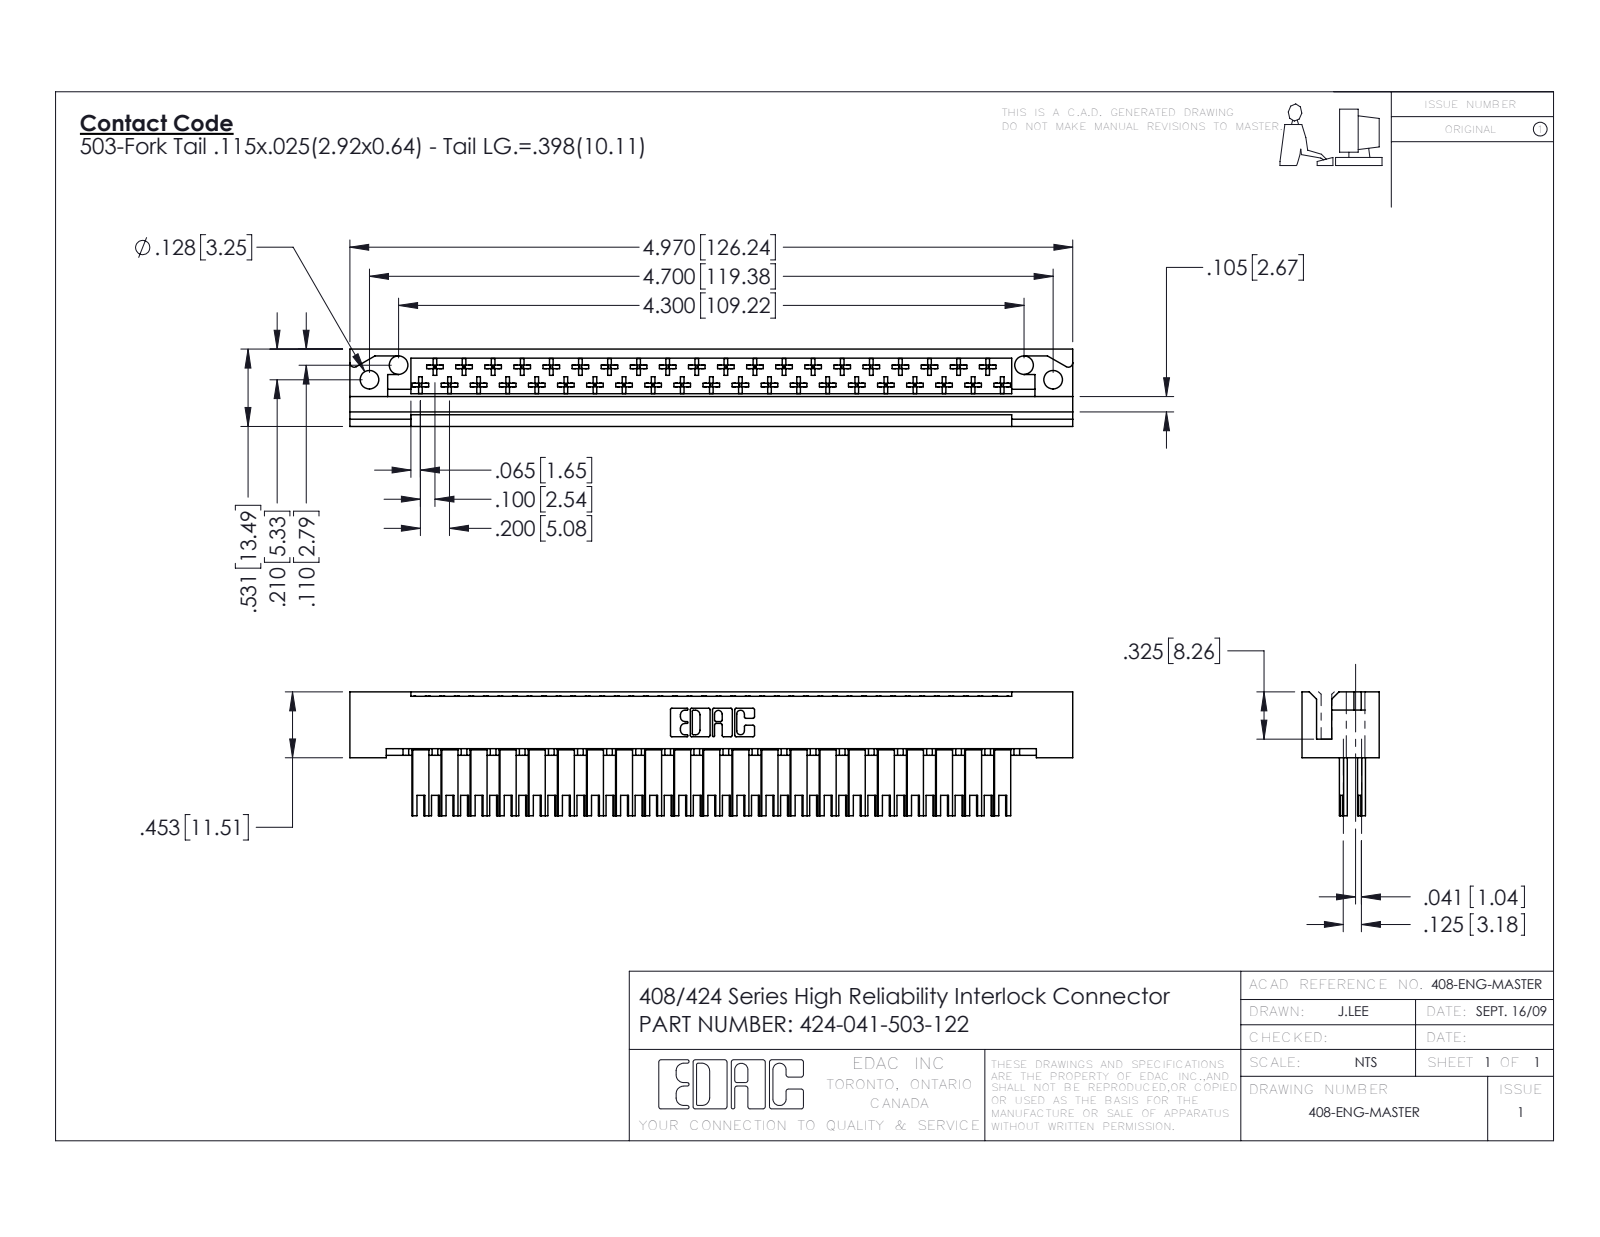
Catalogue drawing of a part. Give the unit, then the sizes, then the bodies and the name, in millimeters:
Units: millimetres
Overall size (bounding box): 126.2 × 21.6 × 13.5
Round holes (diameter × count): ⌀3.3 ×4
Partial cylindrical surfaces — rounded edges, fillets, slot ends (radius × count): R0.3 ×246, R0.5 ×43, R0.3 ×22, R0.2 ×6, R0.8 ×6, R0.7 ×3, R0.8 ×2
Main face-to-face distances: 2.5, 7.5, 0.6, 13.5, 3.2, 6, 6.6, 6.9, 0.6, 5.5
Hole centre spacings: 5.7, 114.3, 109.2, 119.4
Volume: 13 600 mm³ · Surface area: 19 320 mm²
Bodies: 42 solids, 2318 faces (1770 planar, 384 cylindrical, 164 other)
Part name (STEP PRODUCT): 408-290-001_408-290-103; 424 Part_041; 424-047-503-122
STEP written by: SolidWorks 2016 (CONFIG_CONTROL_DESIGN)
